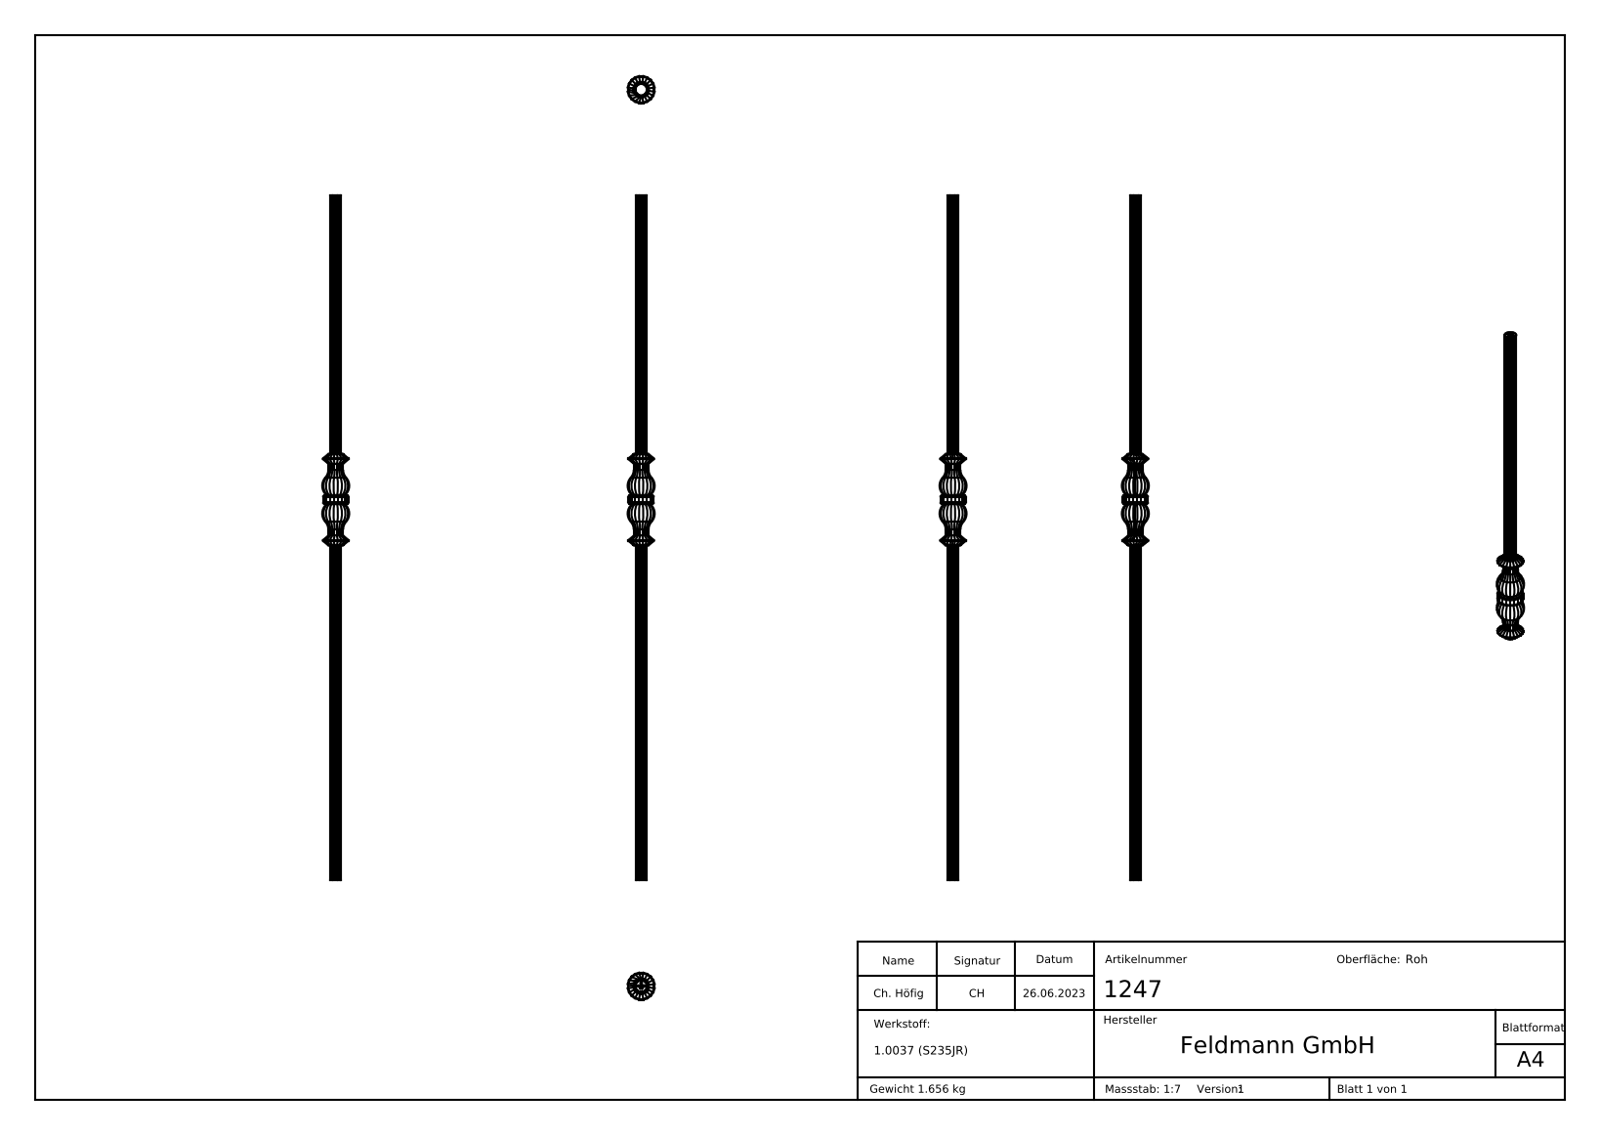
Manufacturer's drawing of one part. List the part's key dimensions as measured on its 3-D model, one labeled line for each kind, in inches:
Part name (STEP PRODUCT): 1247
STEP written by: SolidWorks 2018 (CONFIG_CONTROL_DESIGN)
Units: inches
Bodies: 1 solid, 760 faces (386 planar, 278 cylindrical, 96 other)
Overall size (bounding box): 35.433 × 1.401 × 1.401
Volume: 12.95 in³ · Surface area: 78.76 in²
Partial cylindrical surfaces — rounded edges, fillets, slot ends (radius × count): R0.059 ×112, R0.02 ×48, R0.591 ×40, R0.64 ×40
Main face-to-face distances: 0.583, 0.369, 0.953, 0.094, 0.276, 1.046, 0.677, 0.88, 1.322, 0.771
